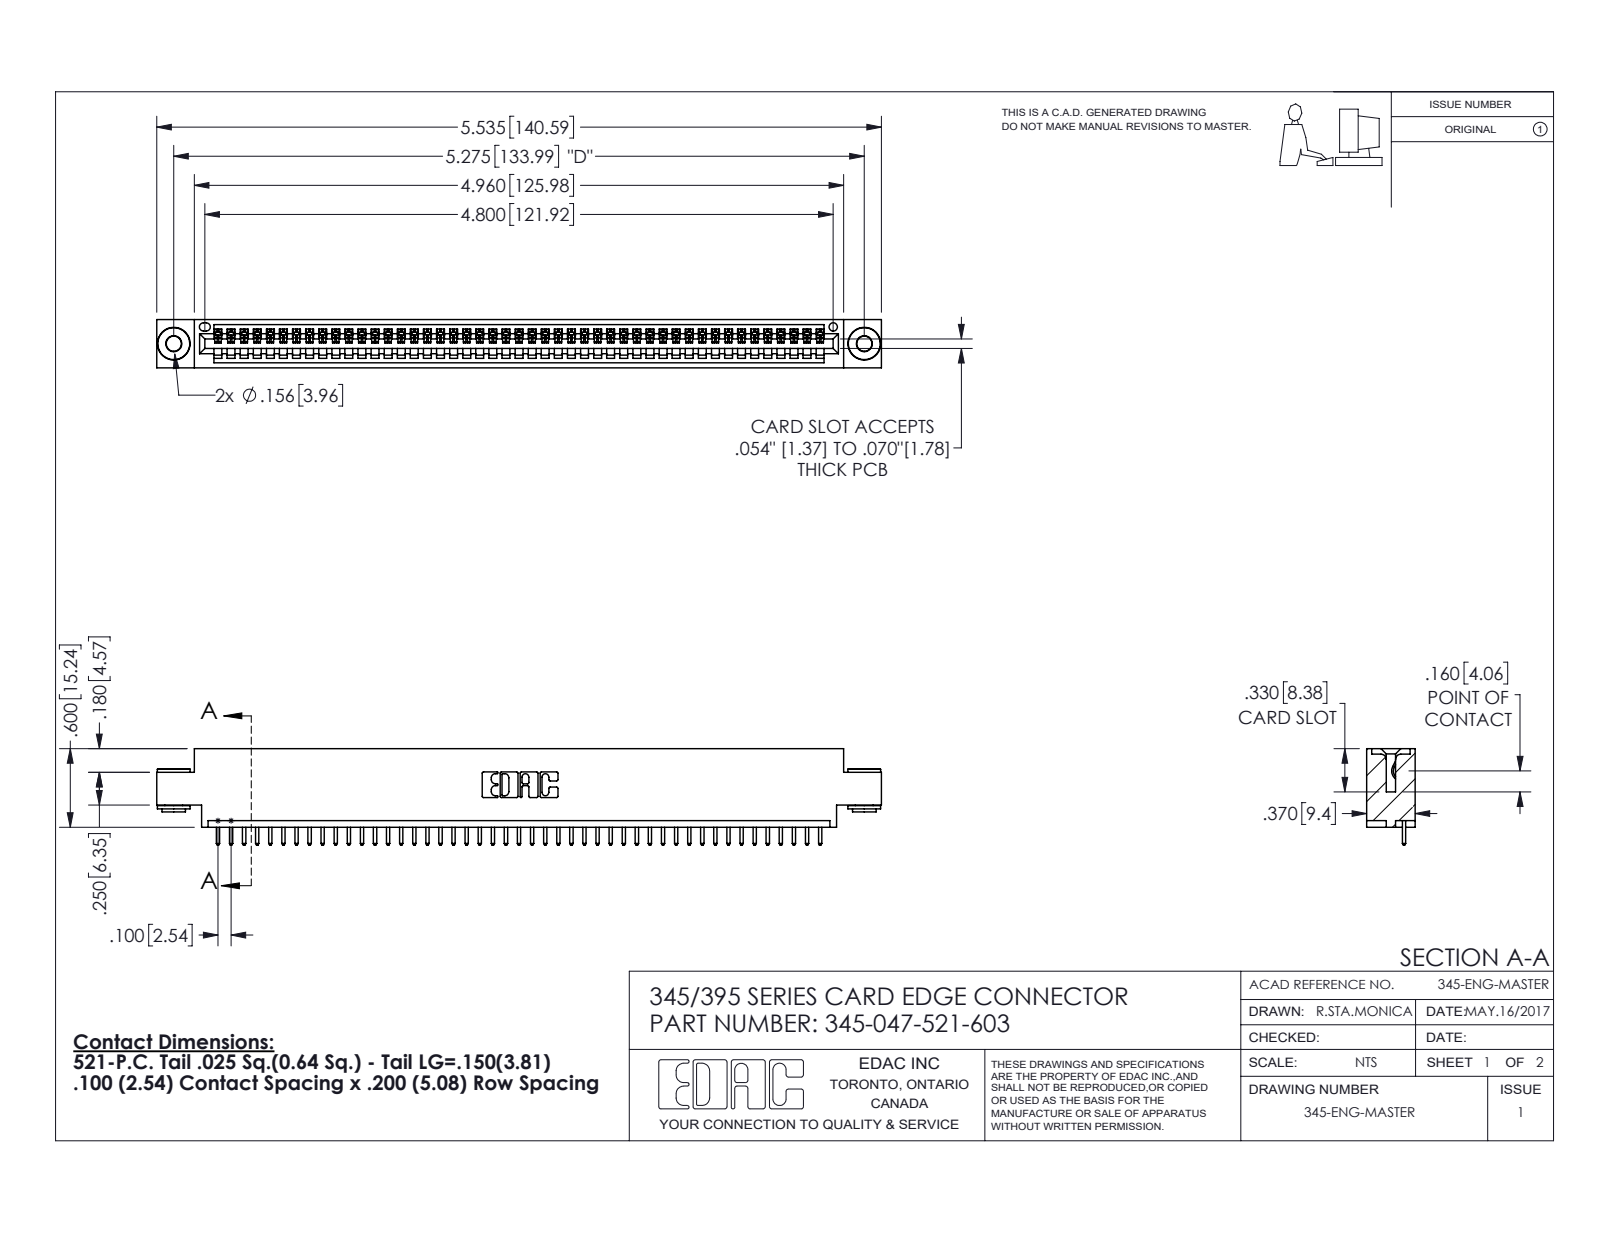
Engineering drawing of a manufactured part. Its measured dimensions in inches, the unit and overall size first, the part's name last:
Units: inches
Overall size (bounding box): 5.535 × 0.737 × 0.37
Round holes (diameter × count): ⌀0.116 ×2, ⌀0.156 ×2, ⌀0.064 ×1
Round bosses / shafts (diameter × count): ⌀0.25 ×2, ⌀0.18 ×2, ⌀0.136 ×2
Partial cylindrical surfaces — rounded edges, fillets, slot ends (radius × count): R0.006 ×94, R0.01 ×94, R0.01 ×22, R0.007 ×6, R0.031 ×6, R0.026 ×3, R0.031 ×2, R0.04 ×2
Main face-to-face distances: 0.072, 0.298, 0.37, 0.2, 0.098, 0.272, 0.025, 0.225, 0.175, 0.149
Hole centre spacings: 0.27, 5.039, 5.275
Volume: 0.803 in³ · Surface area: 26.94 in²
Bodies: 50 solids, 2894 faces (1974 planar, 912 cylindrical, 8 other)
Part name (STEP PRODUCT): 345-047-521-603; 345 Part_0.170 Offset - 0.156 Dia-TH; 345-250-002_345-250-002-102; 345-292-001_345-293-121
STEP written by: SolidWorks 2016 (CONFIG_CONTROL_DESIGN)
